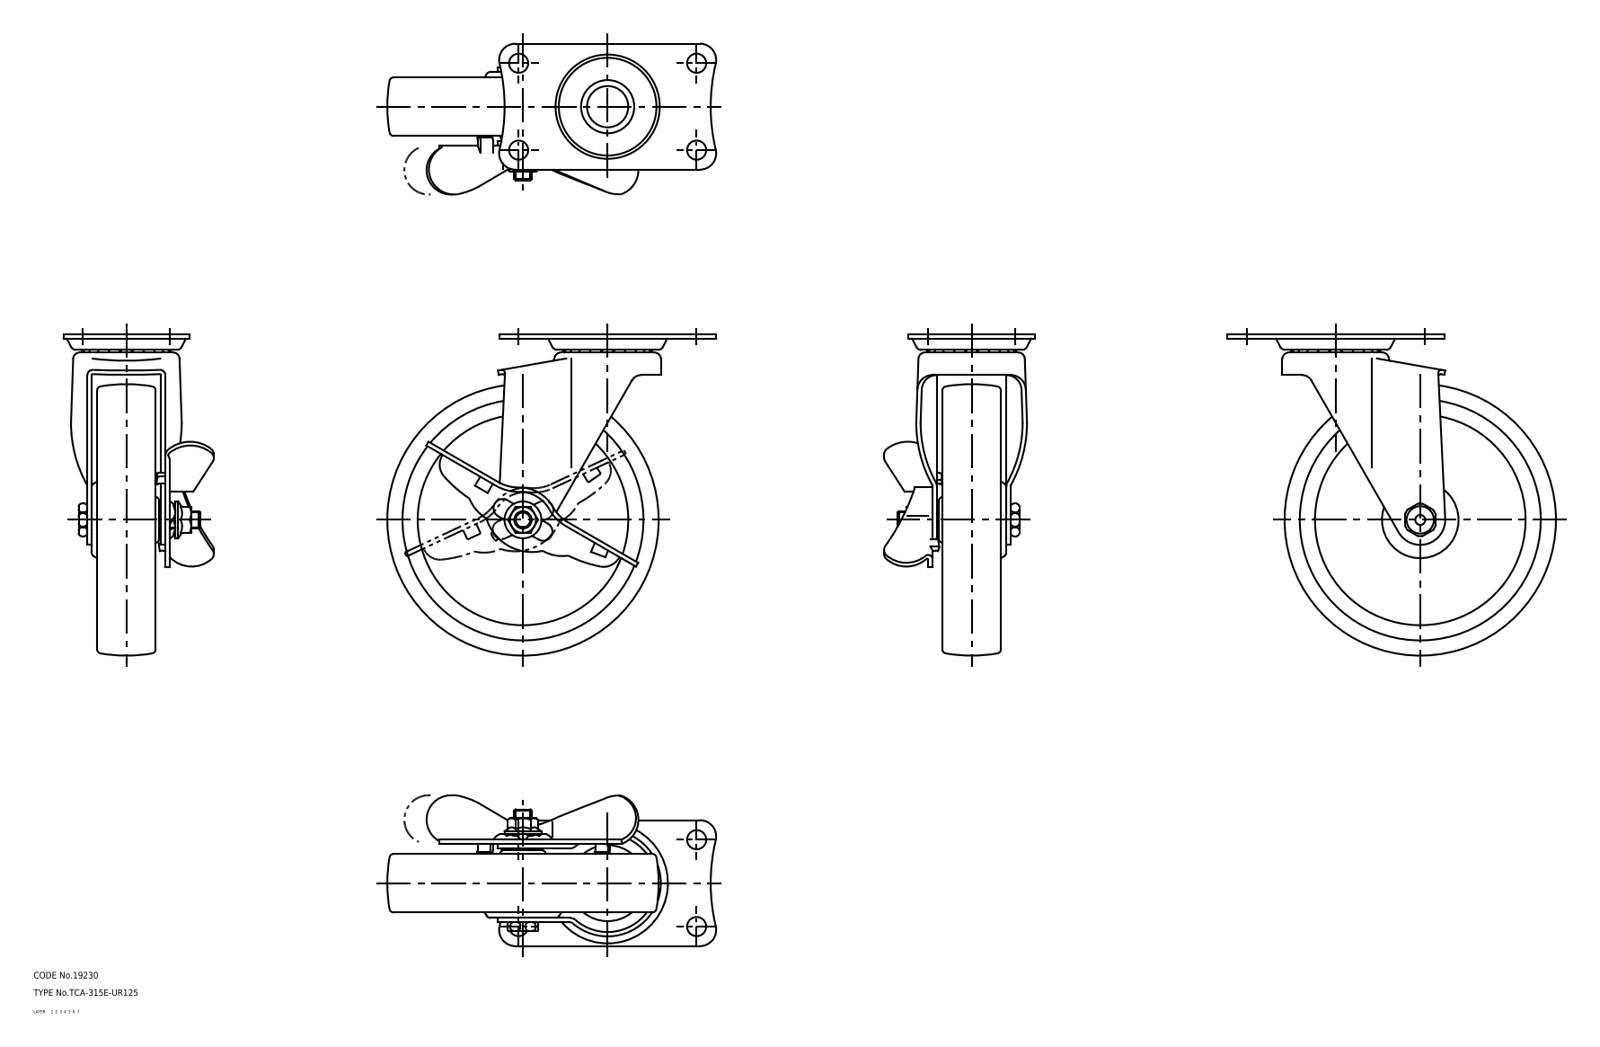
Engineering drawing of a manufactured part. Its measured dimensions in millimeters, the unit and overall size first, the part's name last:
Units: millimetres
Overall size (bounding box): 151.5 × 148 × 69.45
Volume: 294 215 mm³ · Surface area: 87 896 mm²
Bodies: 6 solids, 489 faces (0 planar, 0 cylindrical, 489 other)
Part name (STEP PRODUCT): 67140826; 67140839; 67140852; 67140865 (+2 more)
STEP written by: CADfix (AUTOMOTIVE_DESIGN)
